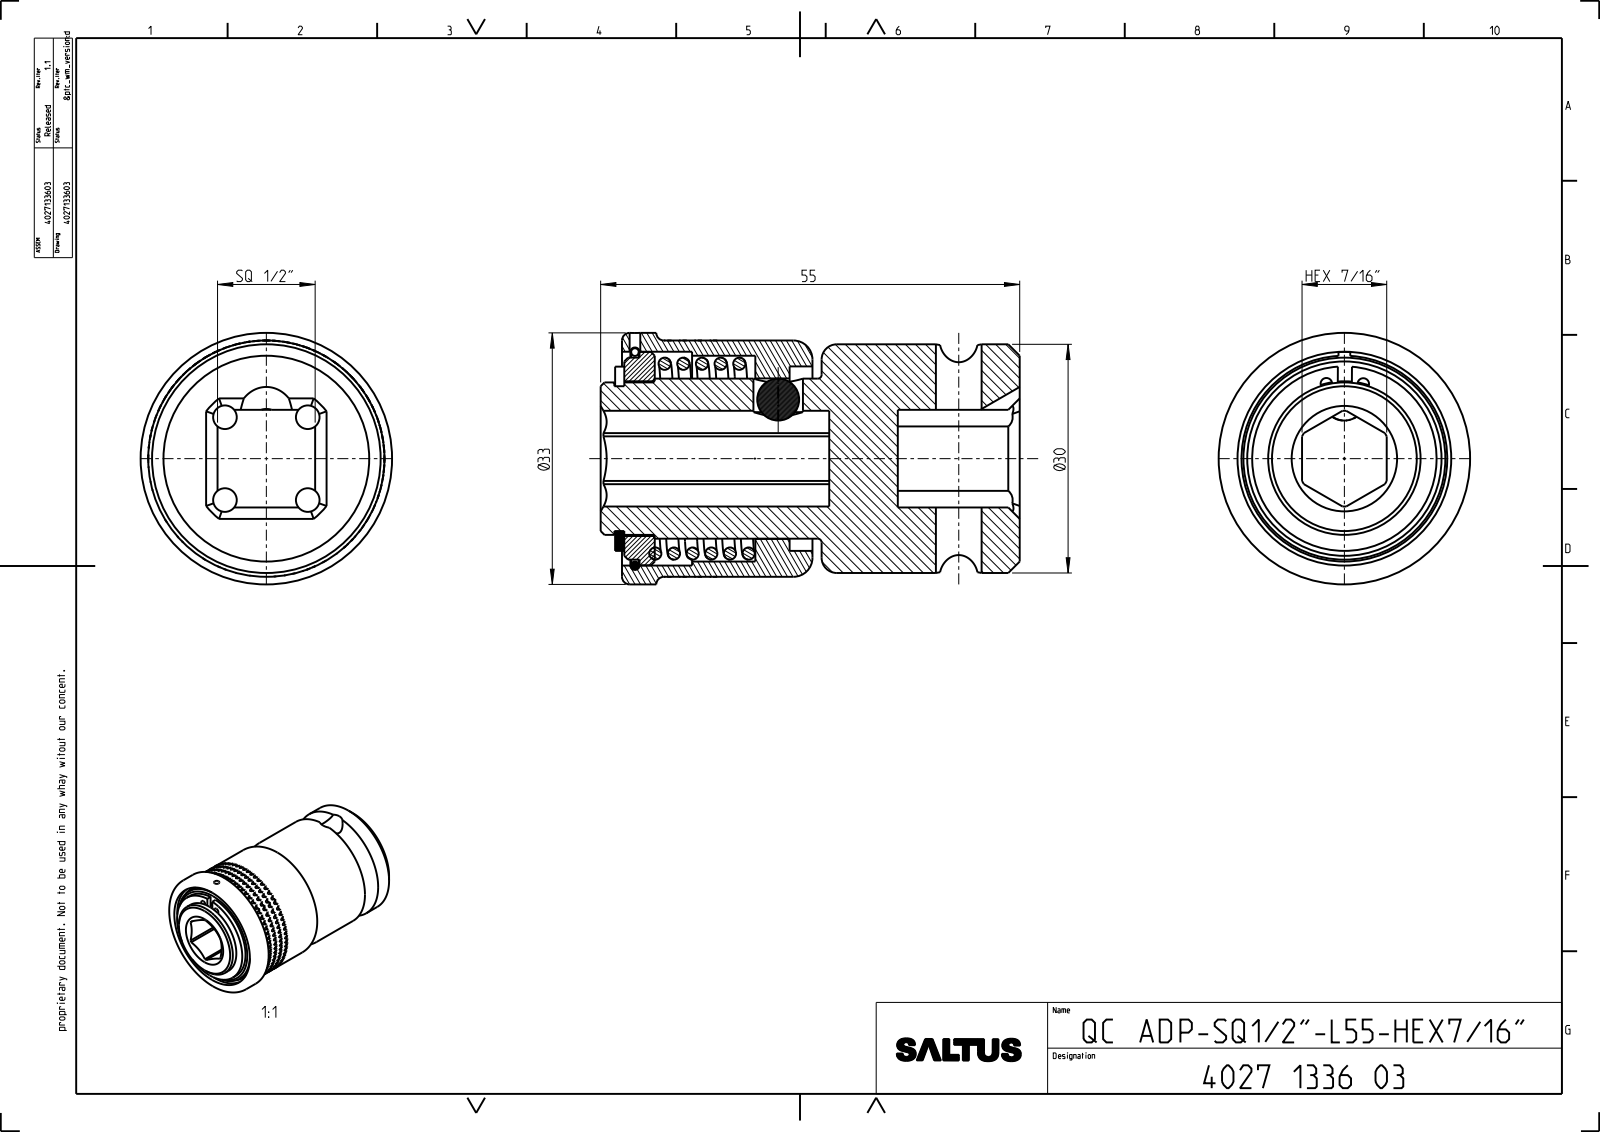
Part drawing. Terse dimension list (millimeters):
name: 4027133603_ASM
written by: CREO PARAMETRIC BY PTC INC, 2022414 (CONFIG_CONTROL_DESIGN)
unit: mm
bodies: 0 solids, 122 faces (32 planar, 50 cylindrical, 40 other)
size: 55 × 33 × 33
holes: 2× ⌀1.52, 1× ⌀1.4, 1× ⌀6, 1× ⌀6.5, 1× ⌀24.2, 1× ⌀28.05
bosses: 1× ⌀33, 1× ⌀31, 1× ⌀30, 1× ⌀26.5, 1× ⌀21, 1× ⌀20, 1× ⌀19
rounds: 4× R1.55, 1× R4, 1× R6.28
face distances: 11.12, 1.2, 25.9, 51.9, 27.2, 12.81, 53.1, 26, 25, 27.1
hole spacings: 4.84, 10.1, 10.11, 18.8, 23.7, 42.5
